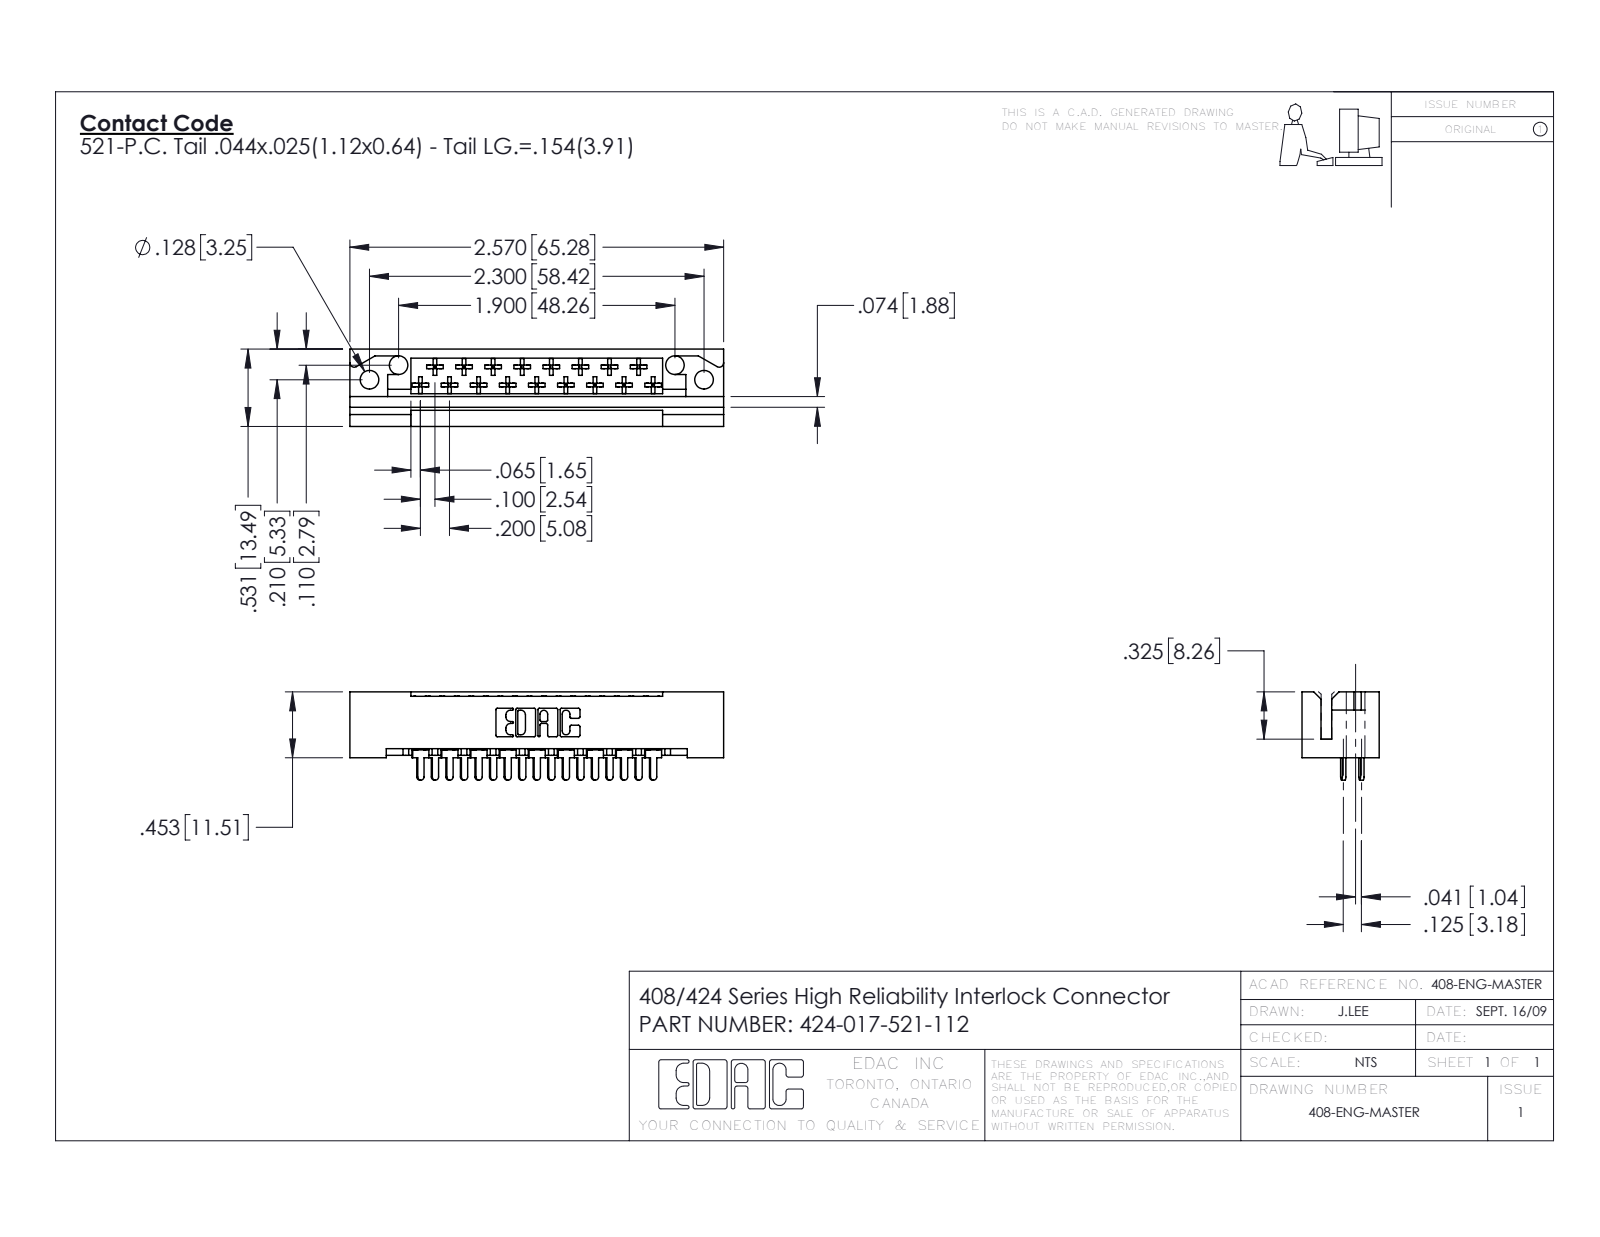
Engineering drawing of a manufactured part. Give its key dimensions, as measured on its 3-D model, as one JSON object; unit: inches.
{"part_name": "424-017-521-112; 408-290-001_408-290-121; 424 Part_017", "step_written_by": "SolidWorks 2016 (CONFIG_CONTROL_DESIGN)", "units": "inches", "bodies": {"solids": 18, "faces": 1080, "planar": 803, "cylindrical": 209, "other": 68}, "overall_size": [2.57, 0.607, 0.531], "volume_in3": 0.432, "surface_area_in2": 12.98, "round_holes": [[0.128, 4]], "partial_cylinders_radius": [[0.01, 102], [0.01, 22], [0.02, 19], [0.022, 17], [0.007, 6], [0.031, 6], [0.026, 3], [0.03, 2]], "face_to_face_distances": [0.4, 0.025, 0.531, 0.125, 0.1, 0.131, 0.326, 0.074, 0.205, 0.025], "hole_center_spacings": [0.224, 2.102, 1.9, 2.3]}
